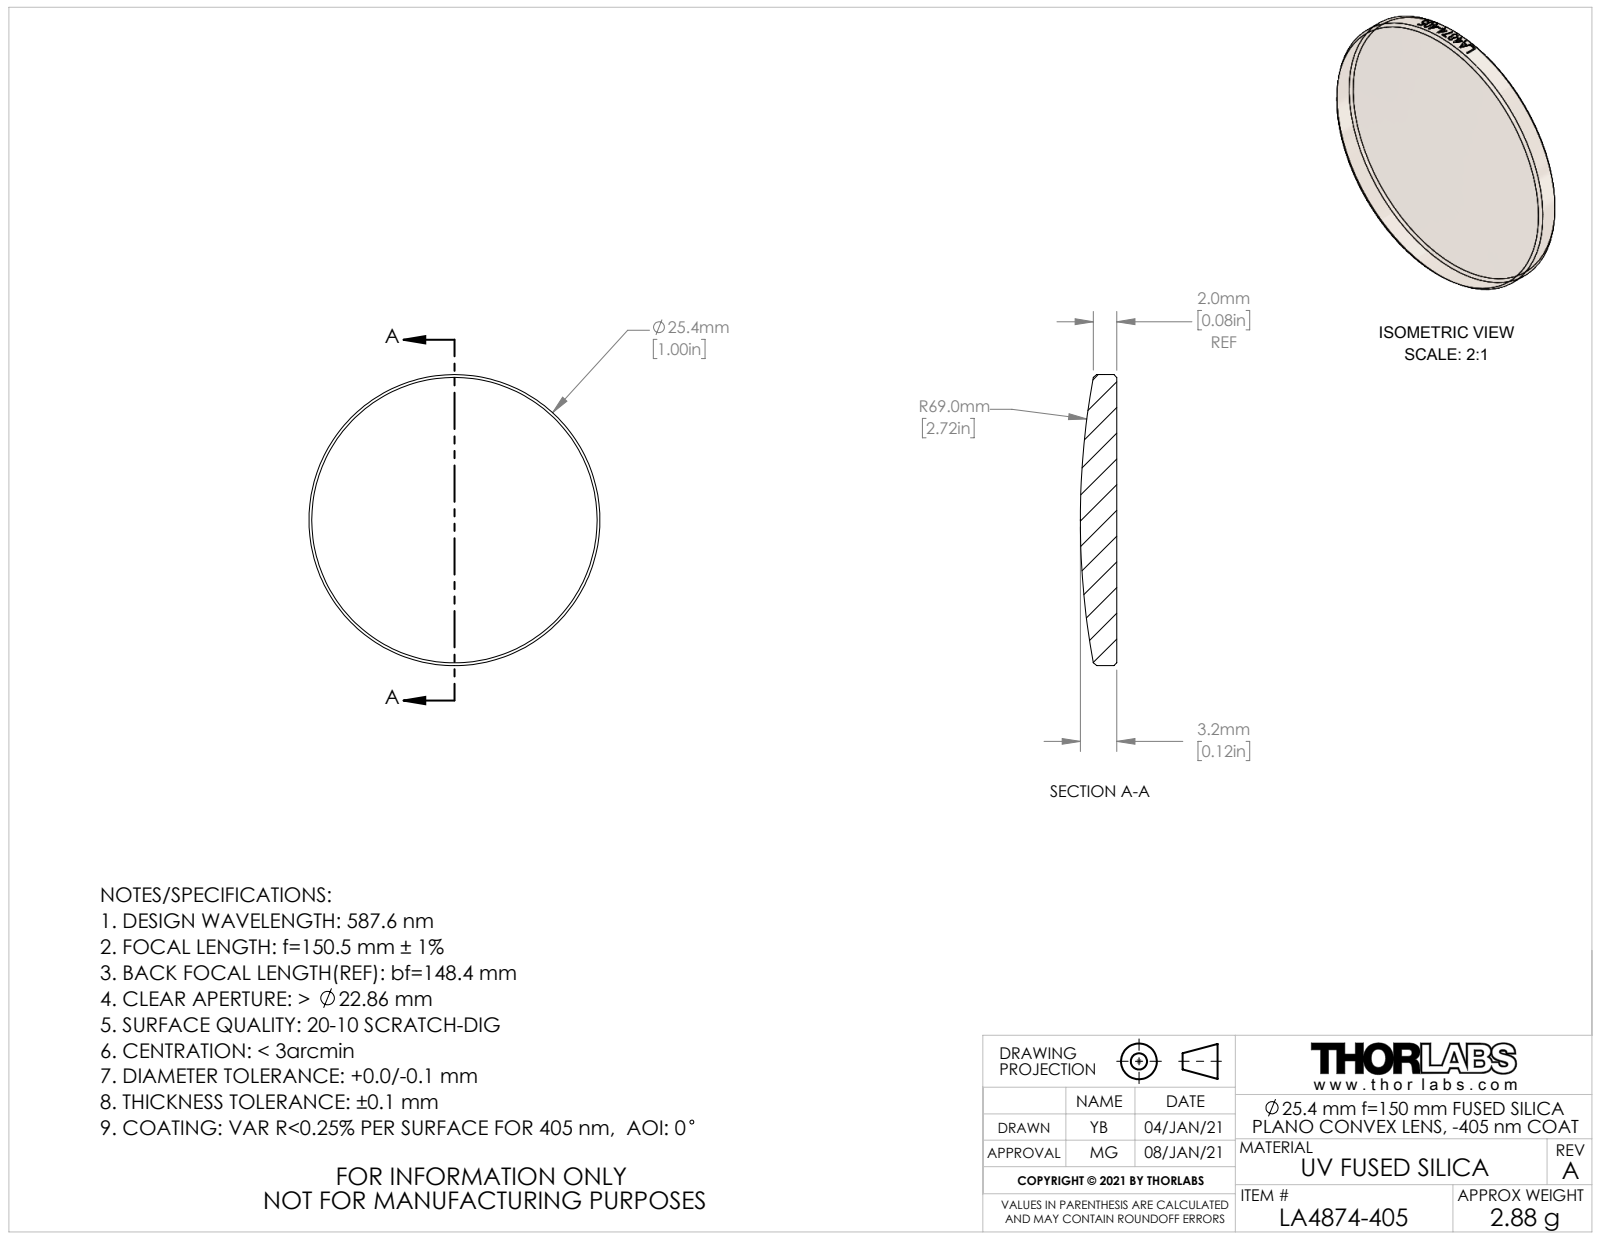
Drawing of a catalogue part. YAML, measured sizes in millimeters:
part_name: "CTN016812-E0W; CTN016832"
step_written_by: "SolidWorks 2018 (AUTOMOTIVE_DESIGN)"
units: millimeters
bodies: {solids: 1, faces: 29, planar: 1, cylindrical: 22, other: 6}
overall_size: [25.4, 25.4, 3.2]
volume: 1300
surface_area: 1156
round_bosses_or_shafts:
  - {diameter: 25.4, count: 1}
